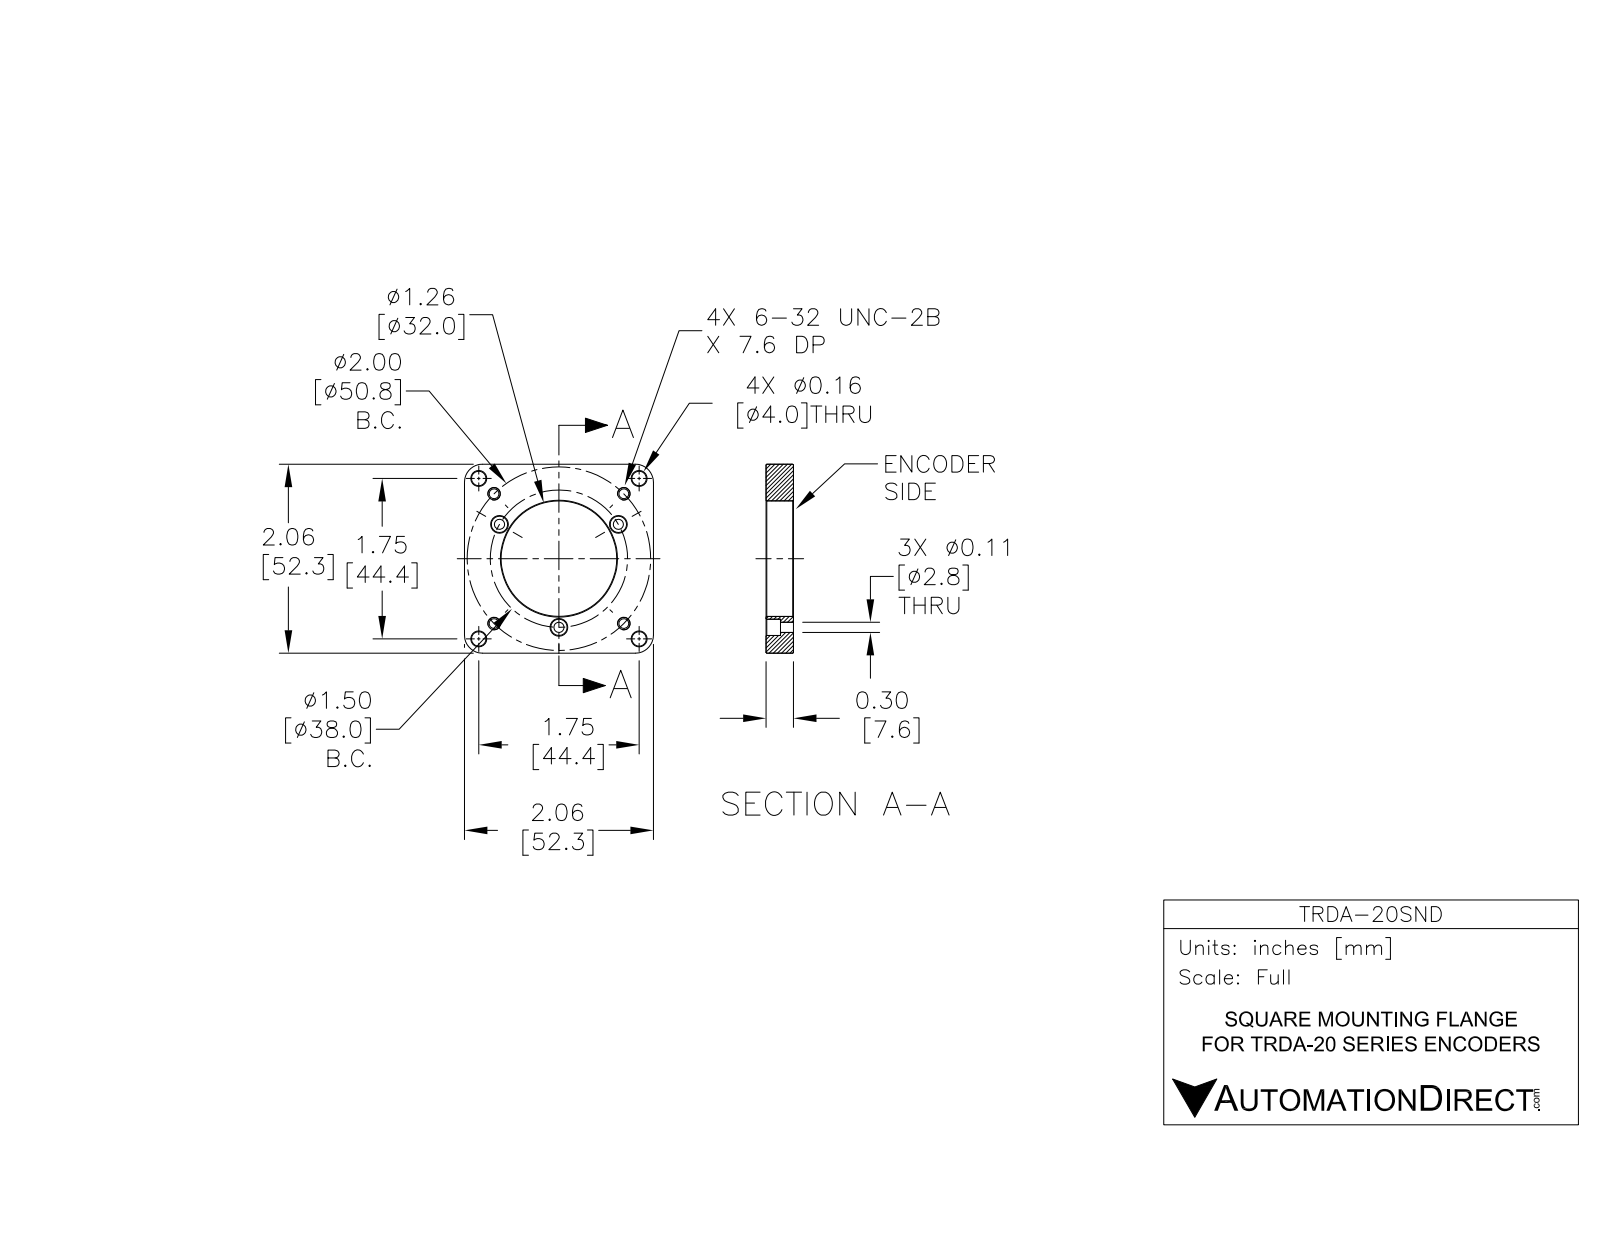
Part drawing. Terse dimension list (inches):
name: TRDA-20SND
written by: SolidWorks 2017 (AUTOMOTIVE_DESIGN)
unit: in
bodies: 5 solids, 109 faces (25 planar, 42 cylindrical, 42 other)
size: 2.059 × 2.059 × 0.299
volume: 0.853 in³; area: 11.08 in²
holes: 4× ⌀0.107, 4× ⌀0.157, 3× ⌀0.11, 3× ⌀0.177, 1× ⌀1.26
bosses: 4× ⌀0.138
rounds: 4× R0.197
face distances: 0.299, 2.059, 1.656, 0.142, 0.157
hole spacings: 1.59, 0.236, 1, 1.236, 1.414, 1.748, 2.236, 0.748
